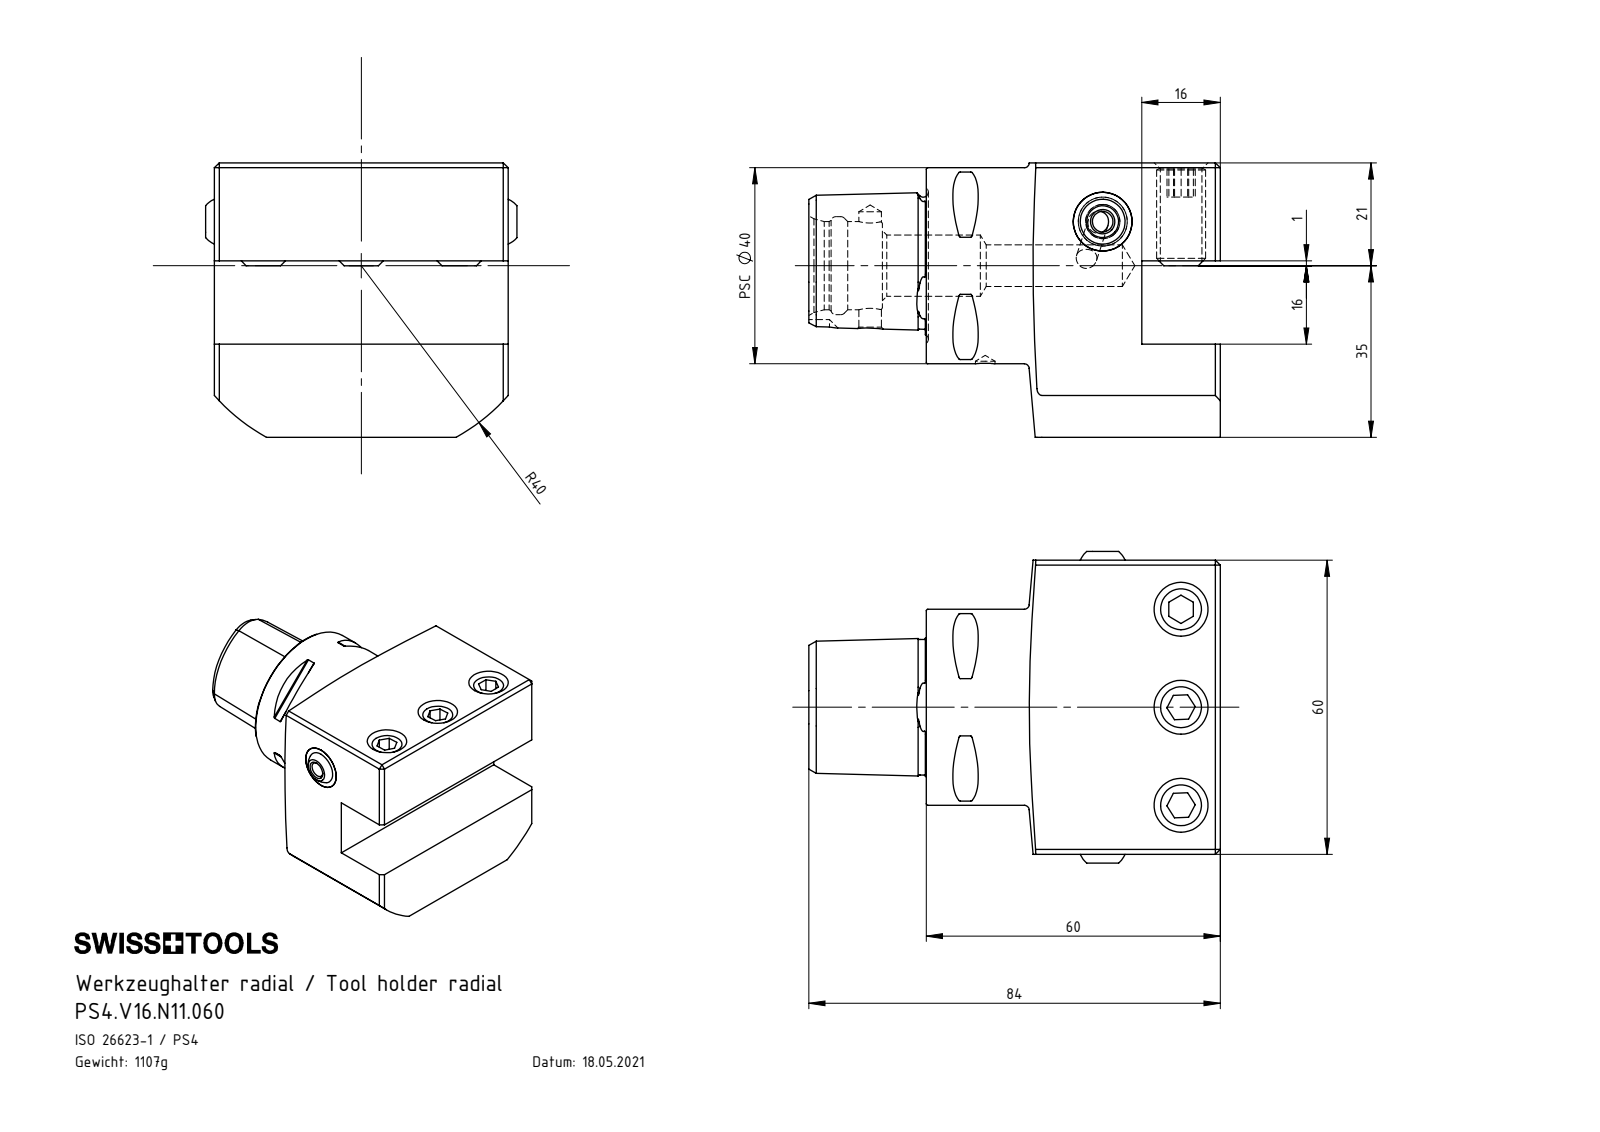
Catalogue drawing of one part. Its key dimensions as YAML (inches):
part_name: "PS4-V16.N11.060; ISO 4026 - M10 x 20_PreviewCfg; KU1-U12.001.010; KU1-U12.001.010_2 (+2 more)"
step_written_by: "SolidWorks 2012 (AUTOMOTIVE_DESIGN)"
units: inches
bodies: {solids: 8, faces: 254, planar: 71, cylindrical: 61, other: 122}
overall_size: [3.307, 2.572, 2.205]
volume: 8.642
surface_area: 46.83
round_holes:
  - {diameter: 0.165, count: 4}
  - {diameter: 0.335, count: 4}
  - {diameter: 0.157, count: 1}
  - {diameter: 0.181, count: 1}
  - {diameter: 0.276, count: 1}
  - {diameter: 0.472, count: 1}
  - {diameter: 0.492, count: 1}
  - {diameter: 0.709, count: 1}
  - {diameter: 0.787, count: 1}
round_bosses_or_shafts:
  - {diameter: 0.394, count: 3}
  - {diameter: 1.575, count: 1}
partial_cylinders:
  - {radius: 0.012, count: 8}
  - {radius: 0.118, count: 1}
  - {radius: 1.575, count: 1}
face_to_face_distances: [2.362, 2.205, 0.63, 0.748, 1.457, 1.417, 0.787, 0.669, 1.732, 0.315]
hole_center_spacings: [0.787, 1.575, 1.761, 2.621, 0.925, 2.5]
